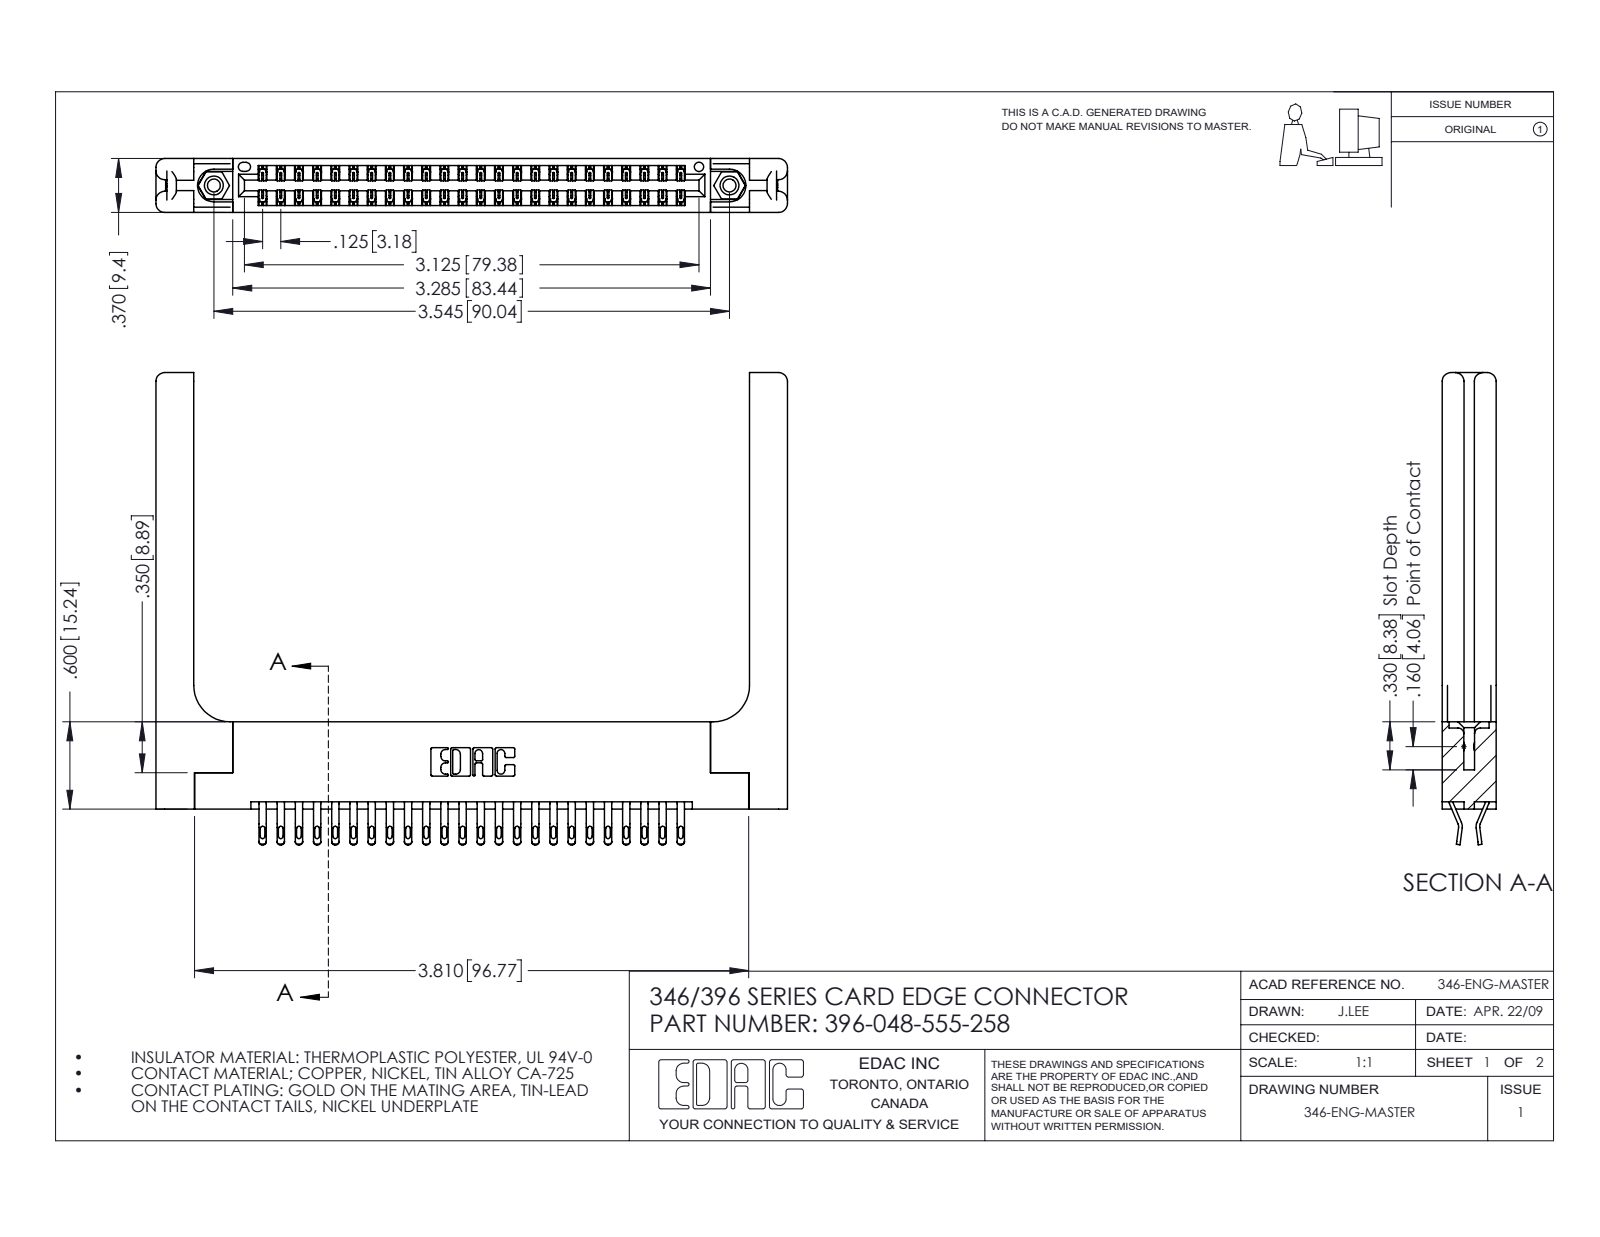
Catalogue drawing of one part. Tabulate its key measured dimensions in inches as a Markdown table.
| quantity | value |
| --- | --- |
| part name | 346-220-058_345-220-058; 346 Part_Flush Mounting Lugs - 0.156 Dia-TH; 396-048-555-258; 345-250-001_345-250-001-102 (+1 more) |
| STEP written by | SolidWorks 2016 (CONFIG_CONTROL_DESIGN) |
| units | inches |
| bodies | 53 solids, 3162 faces (1808 planar, 1294 cylindrical, 60 other) |
| overall size | 4.341 × 3.245 × 0.37 |
| volume | 1.113 in³ |
| surface area | 30.95 in² |
| round holes (diameter × count) | 0.089 × 2, 0.125 × 2, 0.156 × 2, 0.064 × 1 |
| round bosses / shafts (diameter × count) | 0.155 × 2 |
| partial cylindrical surfaces (radius × count) | 0.016 × 96, 0.02 × 96, 0.006 × 72, 0.01 × 22, 0.06 × 16, 0.007 × 6, 0.031 × 6, 0.026 × 3 |
| main face-to-face distances | 0.37, 0.072, 0.048, 0.322, 0.148, 0.15, 0.25, 0.025, 0.298, 0.077 |
| hole center spacings | 0.246, 3.337, 3.545 |
